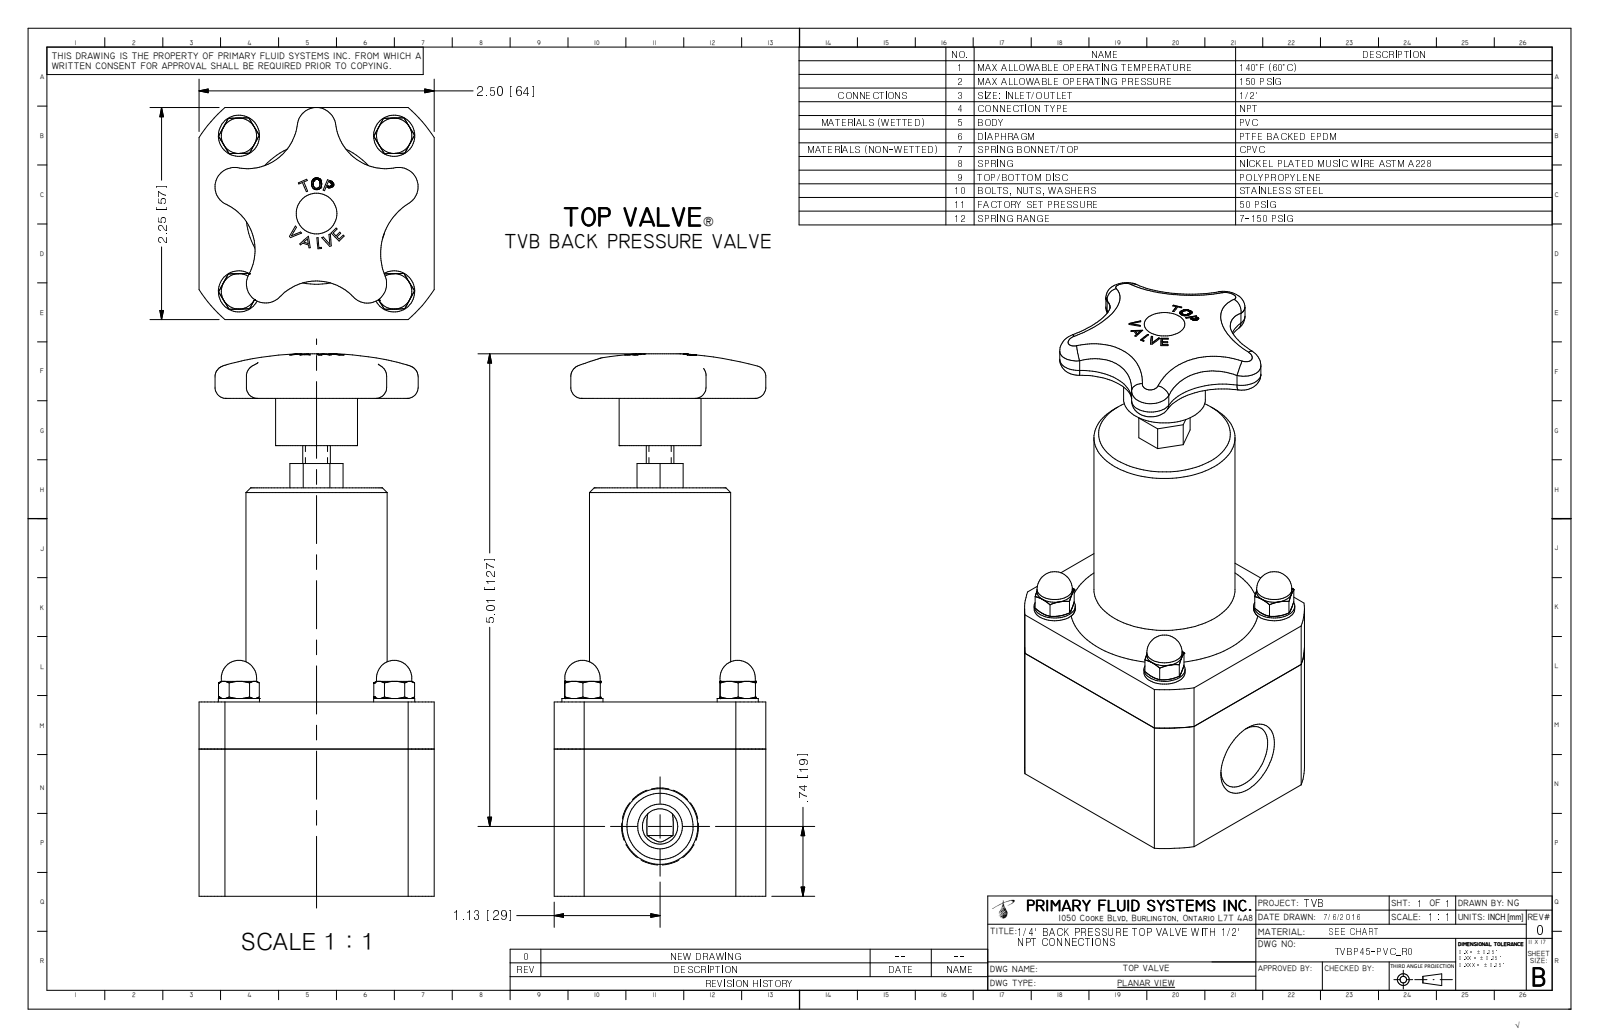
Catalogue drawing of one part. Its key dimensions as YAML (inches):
part_name: "TVBP45-PVC_R0"
step_written_by: "Autodesk Inventor 2009 (AUTOMOTIVE_DESIGN)"
units: inches
bodies: {solids: 1, faces: 337, planar: 140, cylindrical: 45, other: 152}
overall_size: [5.752, 2.5, 2.25]
volume: 16.18
surface_area: 56.18
round_holes:
  - {diameter: 0.147, count: 4}
  - {diameter: 0.703, count: 1}
  - {diameter: 0.719, count: 1}
round_bosses_or_shafts:
  - {diameter: 0.437, count: 4}
  - {diameter: 0.375, count: 4}
  - {diameter: 0.312, count: 4}
  - {diameter: 1.5, count: 1}
  - {diameter: 0.87, count: 1}
  - {diameter: 0.293, count: 1}
partial_cylinders:
  - {radius: 0.085, count: 5}
  - {radius: 0.205, count: 5}
  - {radius: 0.536, count: 4}
  - {radius: 0.656, count: 4}
  - {radius: 0.625, count: 1}
  - {radius: 0.745, count: 1}
  - {radius: 1.488, count: 1}
face_to_face_distances: [2.25, 2.5, 2.06, 4.33, 2.27, 0.6, 1.9, 4.778, 2.718, 0.448]
hole_center_spacings: [1.65, 2.333]
